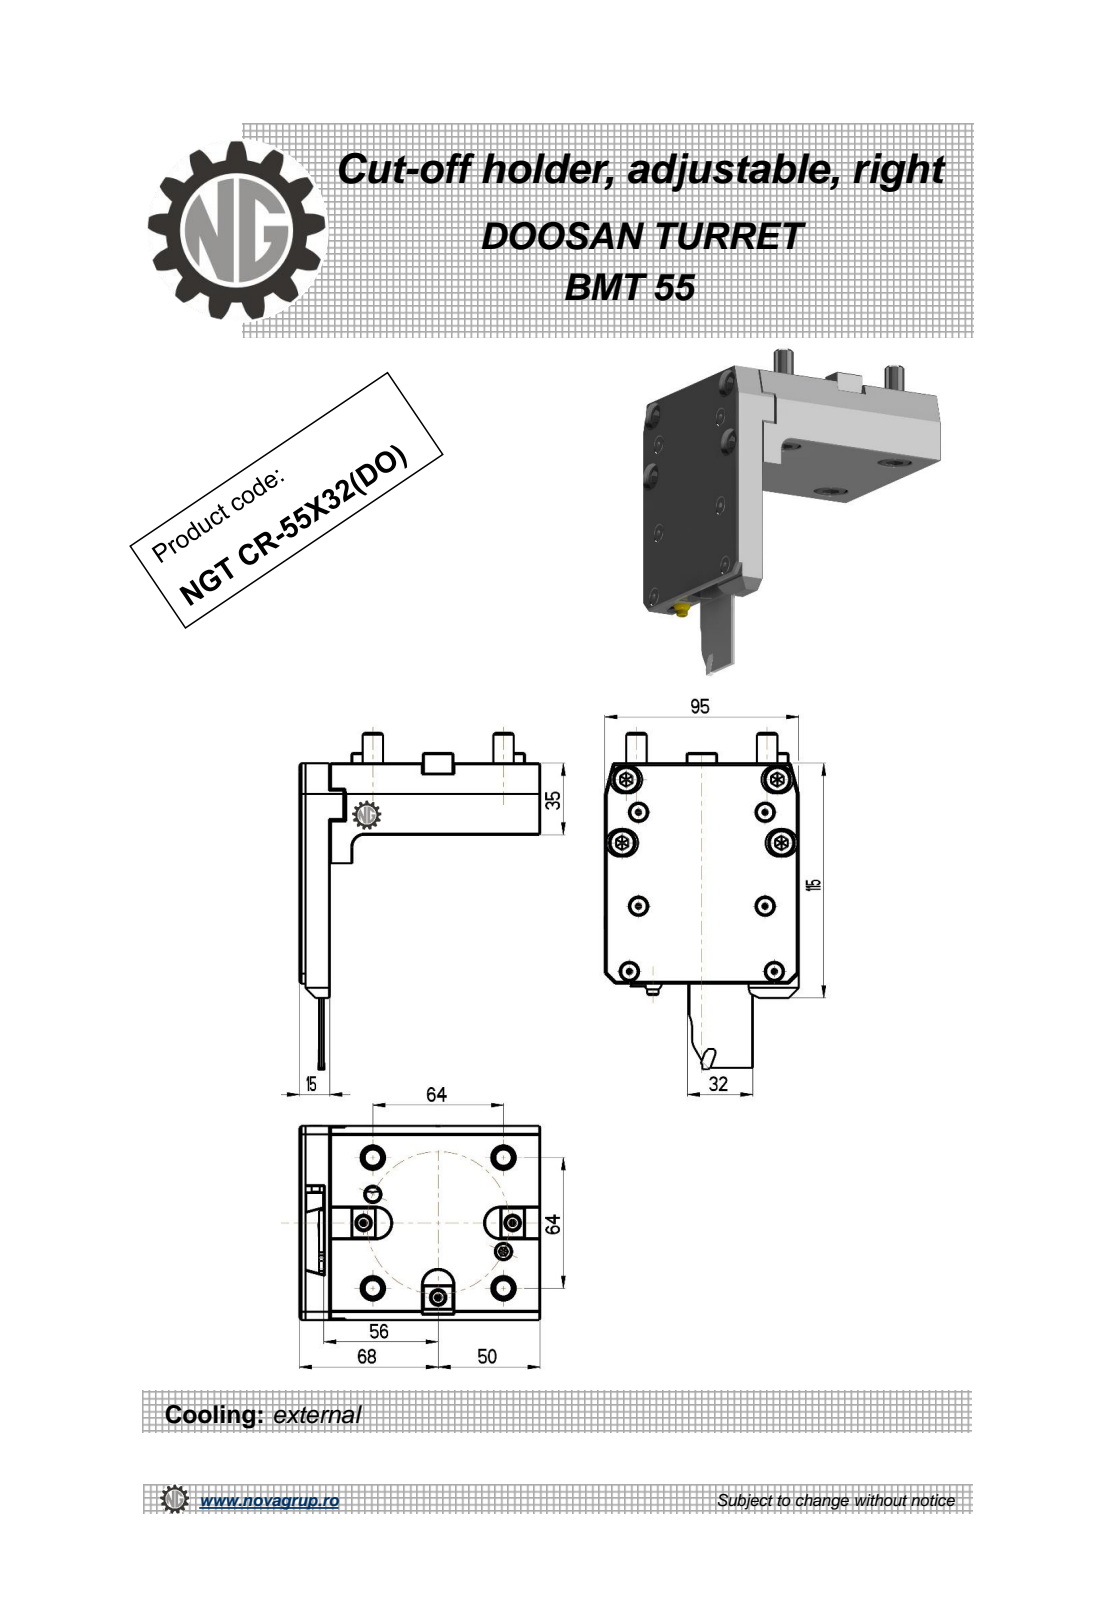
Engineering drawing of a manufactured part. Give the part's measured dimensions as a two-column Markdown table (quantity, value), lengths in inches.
| quantity | value |
| --- | --- |
| part name | NGT_CR_55_32_DO |
| STEP written by | PRO/ENGINEER BY PARAMETRIC TECHNOLOGY CORPORATION, 2010280 (CONFIG_CONTROL_DESIGN) |
| units | inches |
| bodies | 1 solid, 455 faces (290 planar, 93 cylindrical, 72 other) |
| overall size | 5.118 × 4.646 × 3.745 |
| volume | 27.98 in³ |
| surface area | 118.7 in² |
| round holes (diameter × count) | 0.268 × 3, 0.138 × 1 |
| round bosses / shafts (diameter × count) | 0.512 × 4, 0.394 × 4, 0.157 × 3, 0.315 × 2, 0.217 × 1 |
| partial cylindrical surfaces (radius × count) | 0.01 × 24, 0.266 × 8, 0.006 × 6, 0.006 × 6, 0.016 × 6, 0.295 × 3, 0.167 × 2, 0.236 × 1 |
| main face-to-face distances | 0.472, 0.118, 1.378, 0.591, 0.354, 3.74, 4.055, 4.528, 4.173, 4.646 |
| hole center spacings | 1.115, 3.071 |
